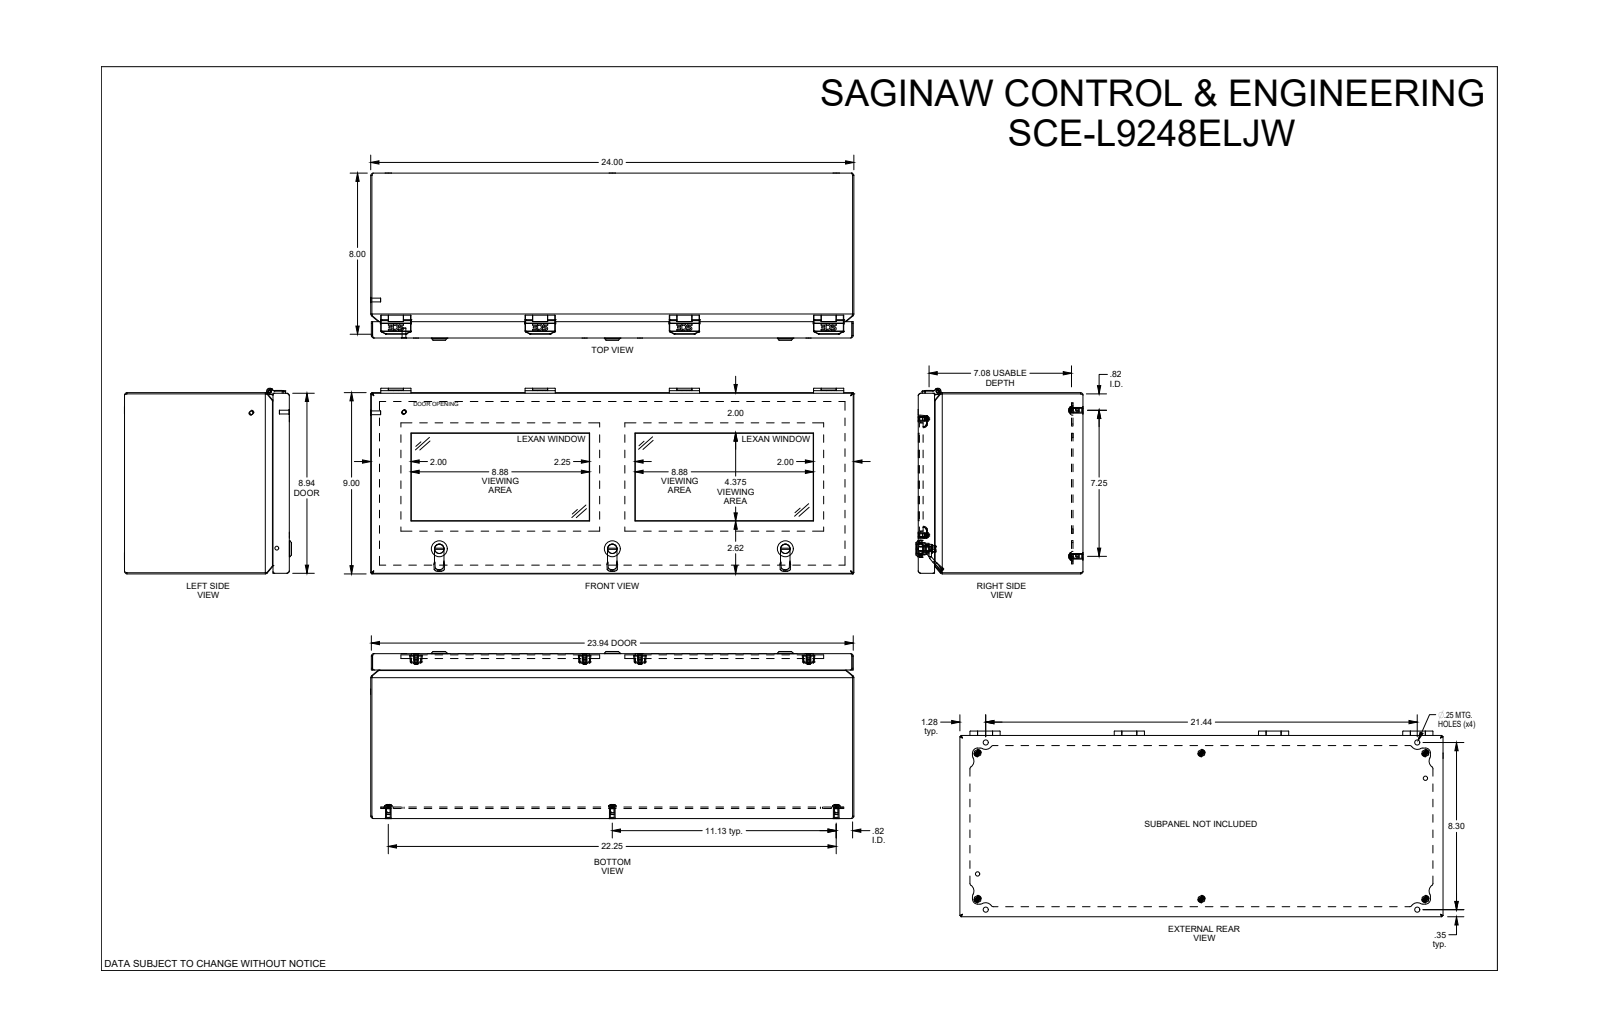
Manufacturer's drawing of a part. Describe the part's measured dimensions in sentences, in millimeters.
The part is named "SCE-L9248ELJWSS". Its 3-D file was written by "SolidWorks 2022 (AUTOMOTIVE_DESIGN)". It is 82 solids with 3039 faces: 1524 planar, 797 cylindrical and 718 other. Overall it measures 609.7 by 234.2 by 210.7 millimeters. Its volume is 1 628 000 cubic millimeters and its surface area 1 683 000 square millimeters. Round holes: 8 of diameter 3.5, 8 of diameter 4, 8 of diameter 5.4, 6 of diameter 4.8, 6 of diameter 6.4, 6 of diameter 7.2, 4 of diameter 4.2, 4 of diameter 4.4, 4 of diameter 6.8, 4 of diameter 8.6, 3 of diameter 5.1, 3 of diameter 6.1. Round bosses or shafts: 8 of diameter 6.7, 8 of diameter 5.4, 8 of diameter 4.8, 6 of diameter 9.5, 6 of diameter 7.1, 4 of diameter 6.6, 4 of diameter 3.8, 3 of diameter 20. Partial cylindrical surfaces (rounded edges, fillets, slot ends): 64 of radius 0.2, 58 of radius 0.5, 42 of radius 1.3, 18 of radius 0.3, 13 of radius 3.2, 13 of radius 6.4, 11 of radius 1.6, 10 of radius 1.5. The main face-to-face distances are 1.5, 227.1, 14.5, 13, 12.6, 11.1, 1.9, 206.4, 204.9, 193.8. The hole center spacings are 182, 282.6, 364.1, 247.9, 44, 182, 282.6, 546.1.
